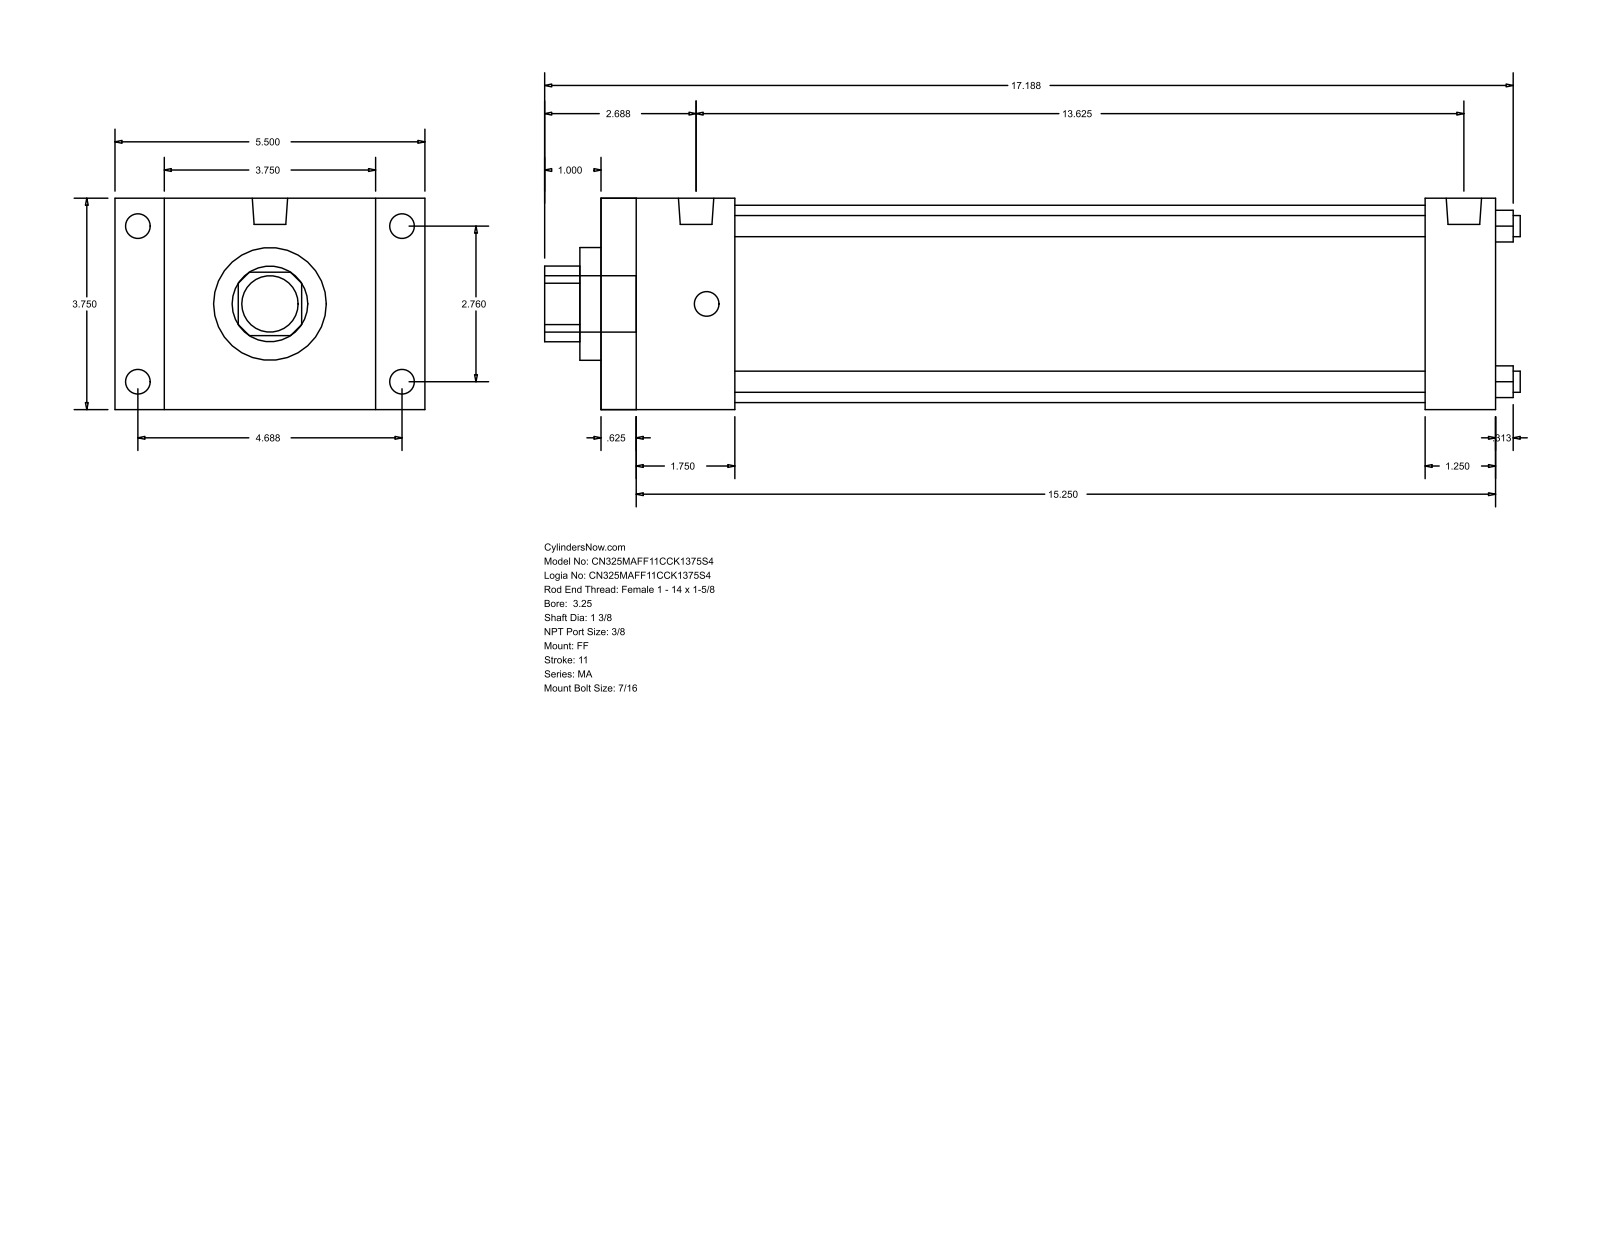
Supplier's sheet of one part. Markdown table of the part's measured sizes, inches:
| quantity | value |
| --- | --- |
| part name | MA_FF__0325_1.375 |
| STEP written by | GSSL Pune (CONFIG_CONTROL_DESIGN) |
| units | inches |
| bodies | 0 solids, 92 faces (64 planar, 28 cylindrical, 0 other) |
| overall size | 17.313 × 5.5 × 3.75 |
| round holes (diameter × count) | 0.375 × 4, 1.375 × 1, 2 × 1, 3.5 × 1 |
| round bosses / shafts (diameter × count) | 0.437 × 8, 0.627 × 2, 1 × 1 |
| partial cylindrical surfaces (radius × count) | 0.672 × 1 |
| main face-to-face distances | 3.75, 15.875, 0.625, 15.25, 0.875, 4.625, 2.375, 14.625, 1.75, 14 |
| hole center spacings | 1.952, 2.76, 3.903 |
